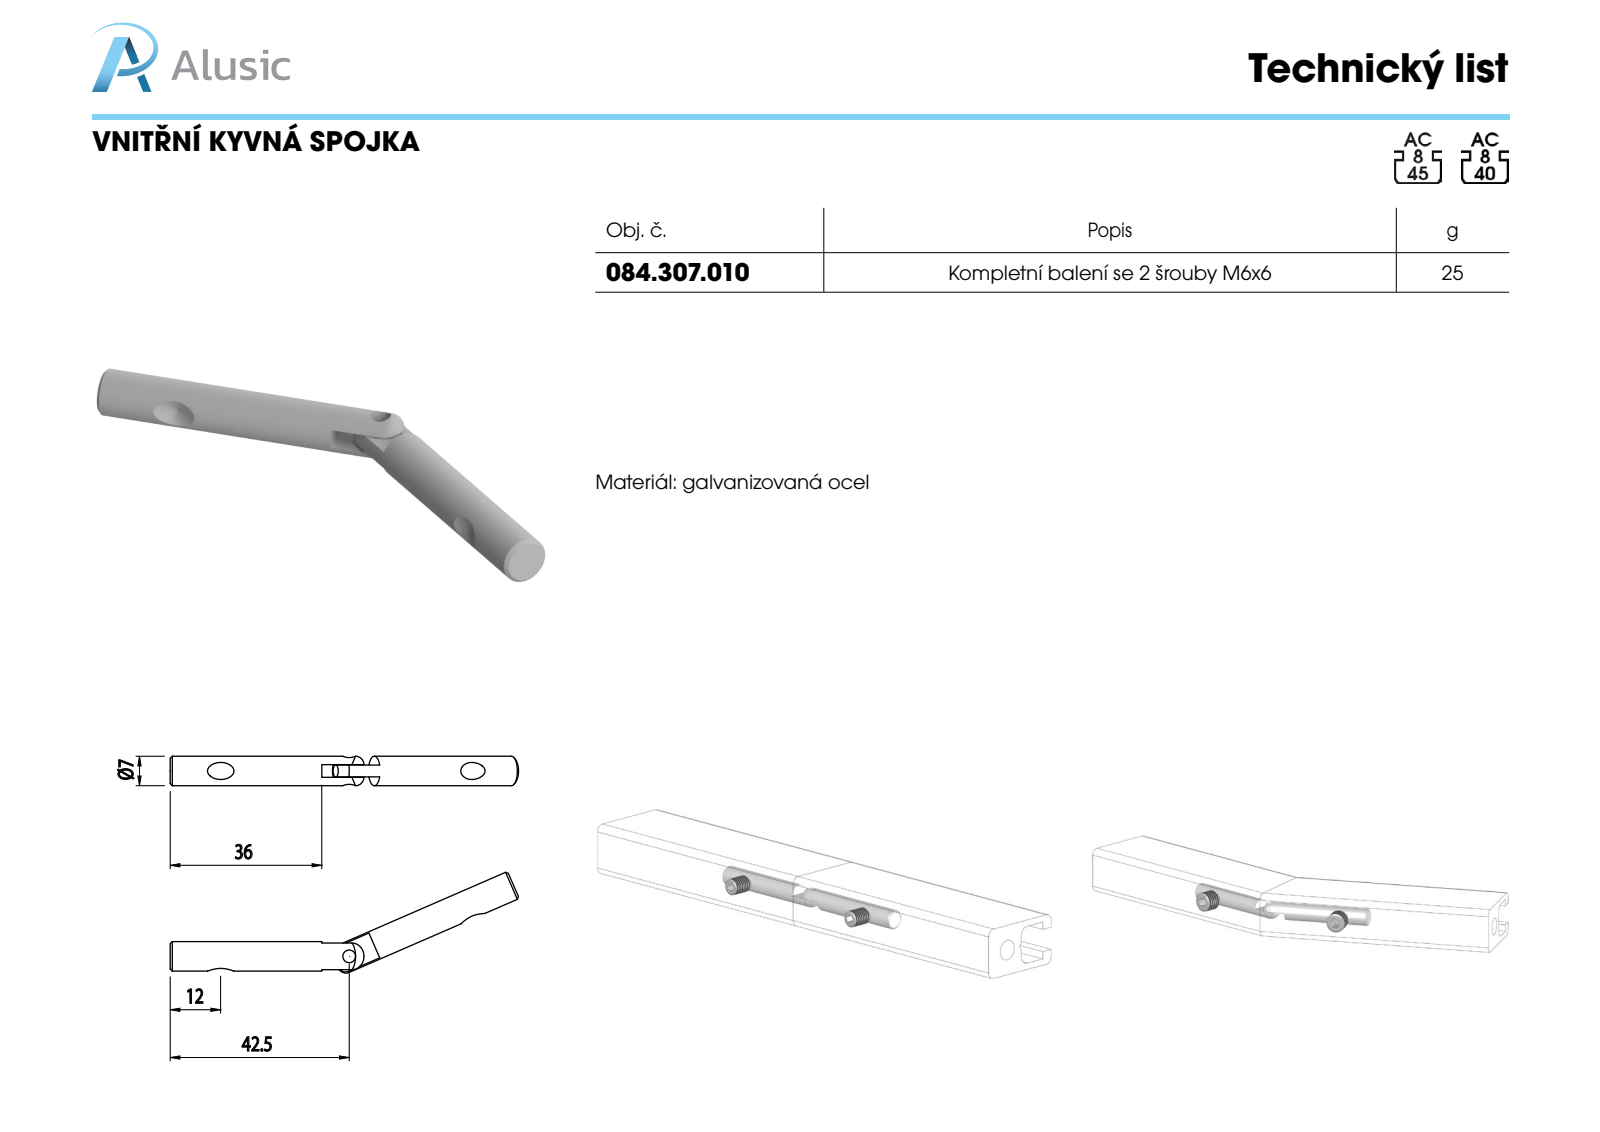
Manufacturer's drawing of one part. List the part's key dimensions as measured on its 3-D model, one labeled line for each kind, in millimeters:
Part name (STEP PRODUCT): 084.307.010; 084.307.010a
STEP written by: SolidWorks 2011 (CONFIG_CONTROL_DESIGN)
Units: millimetres
Bodies: 2 solids, 24 faces (6 planar, 8 cylindrical, 10 other)
Overall size (bounding box): 85 × 7 × 7
Volume: 3 032 mm³ · Surface area: 2 071 mm²
Round holes (diameter × count): ⌀3 ×1
Round bosses / shafts (diameter × count): ⌀7 ×1
Main face-to-face distances: 36, 49, 85, 13
